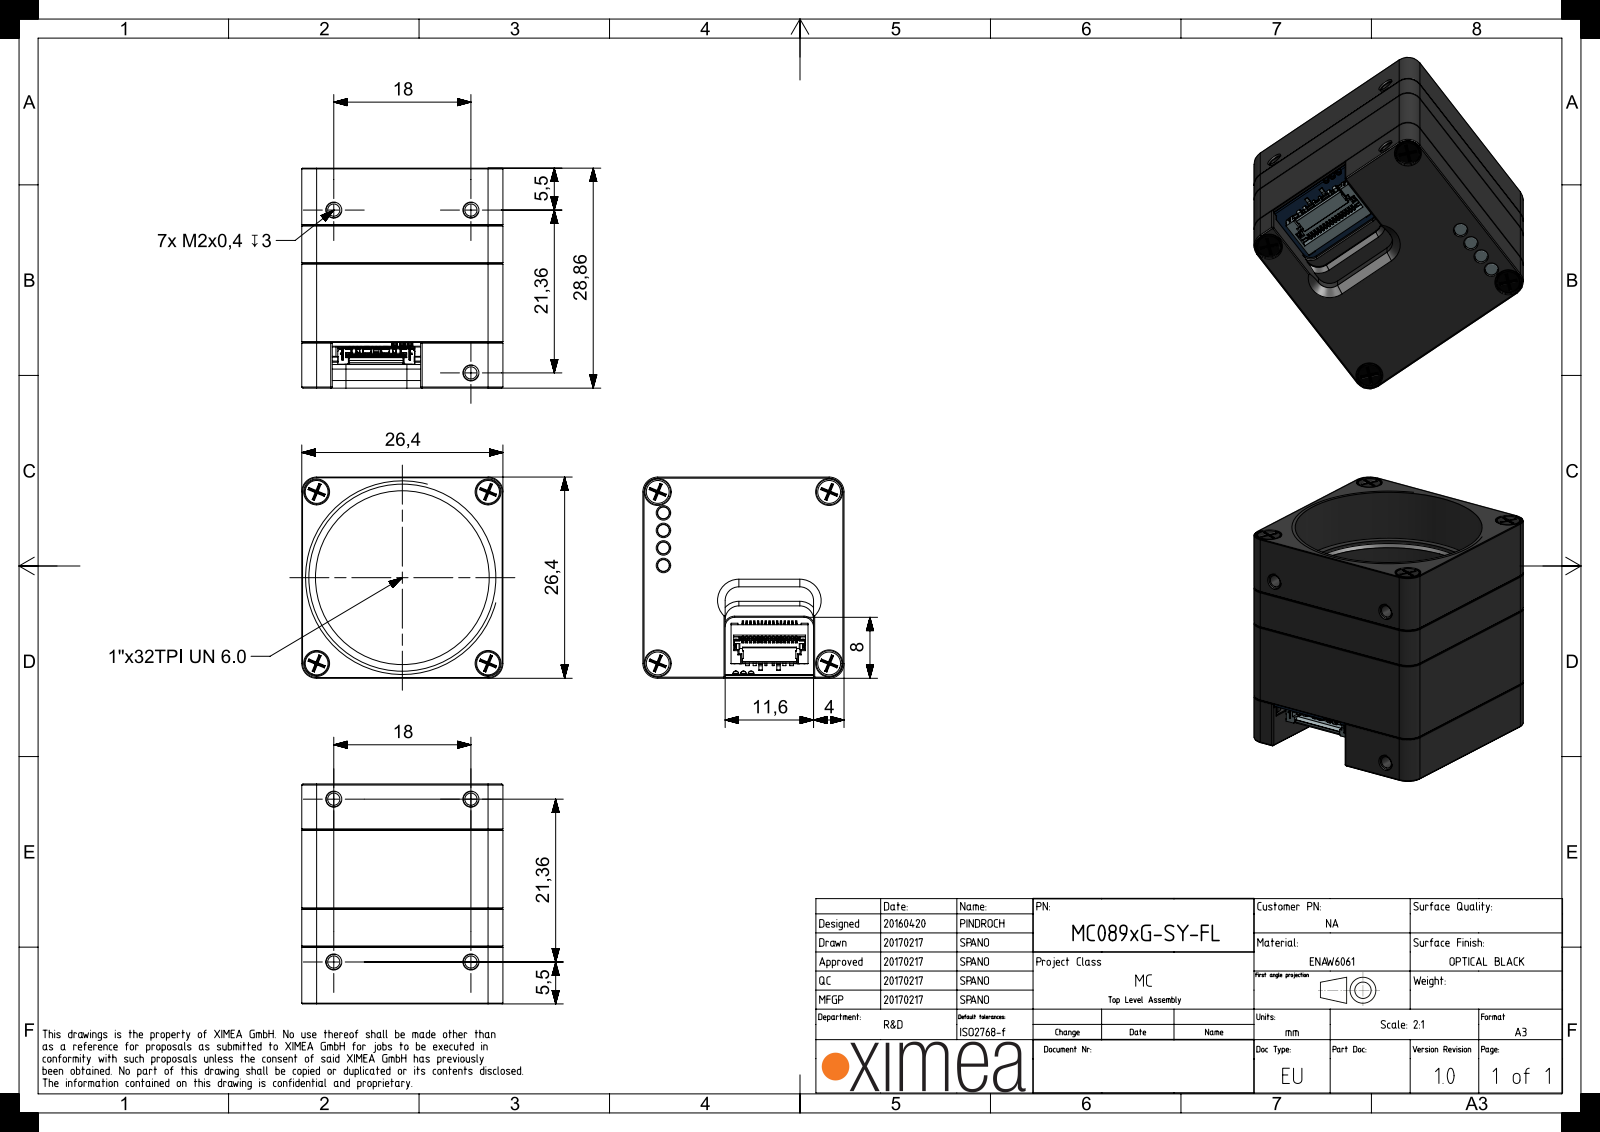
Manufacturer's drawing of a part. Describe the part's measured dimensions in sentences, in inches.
The part is named "MECH-O-RING-22X1-VI370; MT089xG-PR-SENSOR-PCA; FLT-BK7-AR2X-D25; SROB-M1.6x3-SLOT-STNLS (+8 more)". Its 3-D file was written by "SIEMENS PLM Software NX 1907 (AUTOMOTIVE_DESIGN)". It is 32 solids with 7225 faces: 4906 planar, 2024 cylindrical and 295 other. Overall it measures 1.136 by 1.039 by 1.039 inches. Its volume is 0.596 cubic inches and its surface area 26.61 square inches. Round holes: 12 of diameter 0.063, 4 of diameter 0.039, 4 of diameter 0.079, 4 of diameter 0.083, 4 of diameter 0.118, 4 of diameter 0.126, 4 of diameter 0.132, 2 of diameter 0.051, 2 of diameter 0.067, 1 of diameter 0.157, 1 of diameter 0.827, 1 of diameter 0.898. Round bosses or shafts: 4 of diameter 0.075, 4 of diameter 0.064, 4 of diameter 0.033, 2 of diameter 0.118, 2 of diameter 0.063, 1 of diameter 0.984, 1 of diameter 0.85. Partial cylindrical surfaces (rounded edges, fillets, slot ends): 26 of radius 0.039, 17 of radius 0.013, 14 of radius 0.004, 14 of radius 0.006, 12 of radius 0.008, 12 of radius 0.015, 8 of radius 0.01, 8 of radius 0.02. The main face-to-face distances are 0.039, 0.142, 1.039, 0.27, 0.1, 0.181, 0.451, 0.412, 0.408, 0.266. The hole center spacings are 0.626, 0.886, 0.091, 0.148, 0.181, 0.531, 0.709, 0.738.
